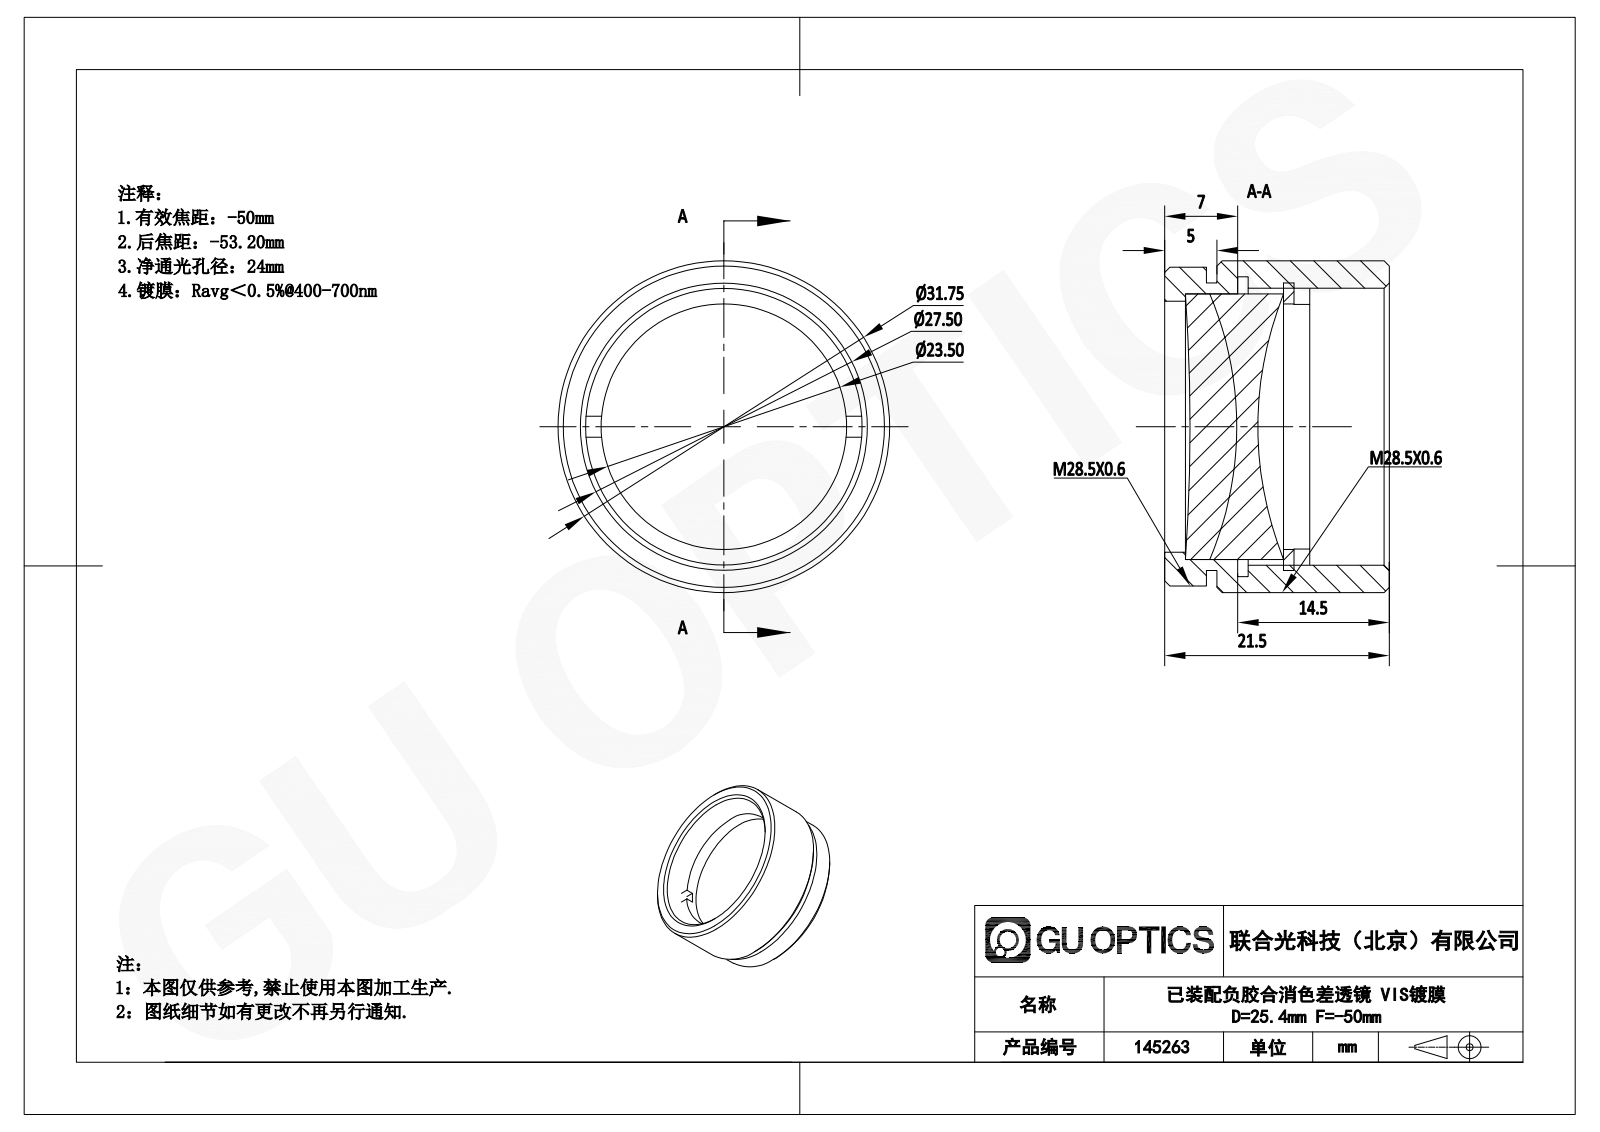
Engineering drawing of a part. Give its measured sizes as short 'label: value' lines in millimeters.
name: 145263
written by: SolidWorks 2020 (CONFIG_CONTROL_DESIGN)
unit: mm
bodies: 4 solids, 54 faces (16 planar, 22 cylindrical, 16 other)
size: 31.75 × 31.75 × 21.5
volume: 9 408 mm³; area: 8 469 mm²
holes: 1× ⌀23.5, 1× ⌀24, 1× ⌀26.5, 1× ⌀28.7
bosses: 1× ⌀31.75, 1× ⌀30.5, 1× ⌀27.5, 1× ⌀25.4
face distances: 3, 2, 1, 4, 5, 11.39, 13.89, 2.5, 21.5, 10.11
